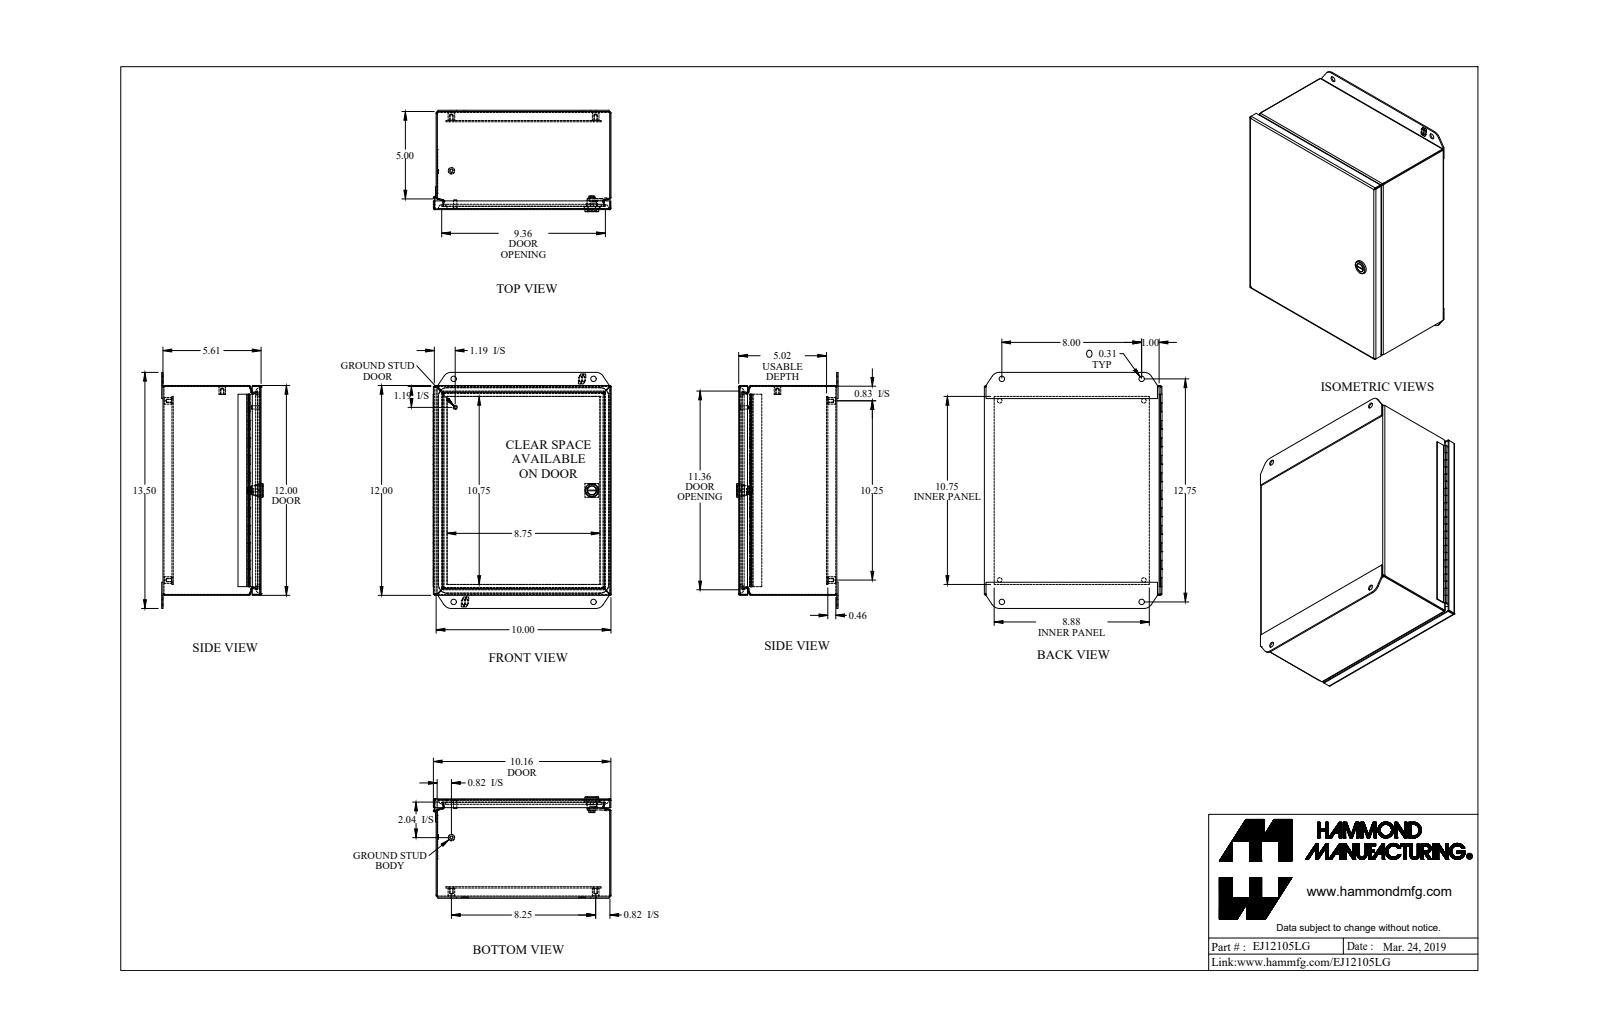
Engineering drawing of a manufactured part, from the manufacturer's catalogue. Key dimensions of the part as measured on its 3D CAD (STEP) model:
Part name (STEP PRODUCT): EJ12105LG_Default
STEP written by: SolidWorks 2019 (CONFIG_CONTROL_DESIGN)
Units: inches
Bodies: 16 solids, 707 faces (393 planar, 222 cylindrical, 92 other)
Overall size (bounding box): 13.5 × 10.165 × 5.805
Volume: 42.61 in³ · Surface area: 1 405 in²
Round holes (diameter × count): ⌀0.156 ×5, ⌀0.265 ×4, ⌀0.313 ×4, ⌀0.05 ×1, ⌀0.516 ×1
Round bosses / shafts (diameter × count): ⌀0.375 ×5, ⌀0.788 ×1, ⌀0.535 ×1, ⌀0.496 ×1, ⌀0.435 ×1, ⌀0.25 ×1, ⌀0.188 ×1, ⌀0.1 ×1
Partial cylindrical surfaces — rounded edges, fillets, slot ends (radius × count): R0.029 ×16, R0.086 ×16, R0.281 ×10, R0.25 ×4, R0.499 ×4, R0.5 ×4, R0.06 ×2, R0.539 ×2
Main face-to-face distances: 0.057, 5.554, 0.072, 0.589, 5.611, 5.497, 9.943, 11.943, 0.46, 0.517
Hole centre spacings: 1.256, 11.501, 10.25, 8.22, 13.158, 14.081, 5.13, 6.376
